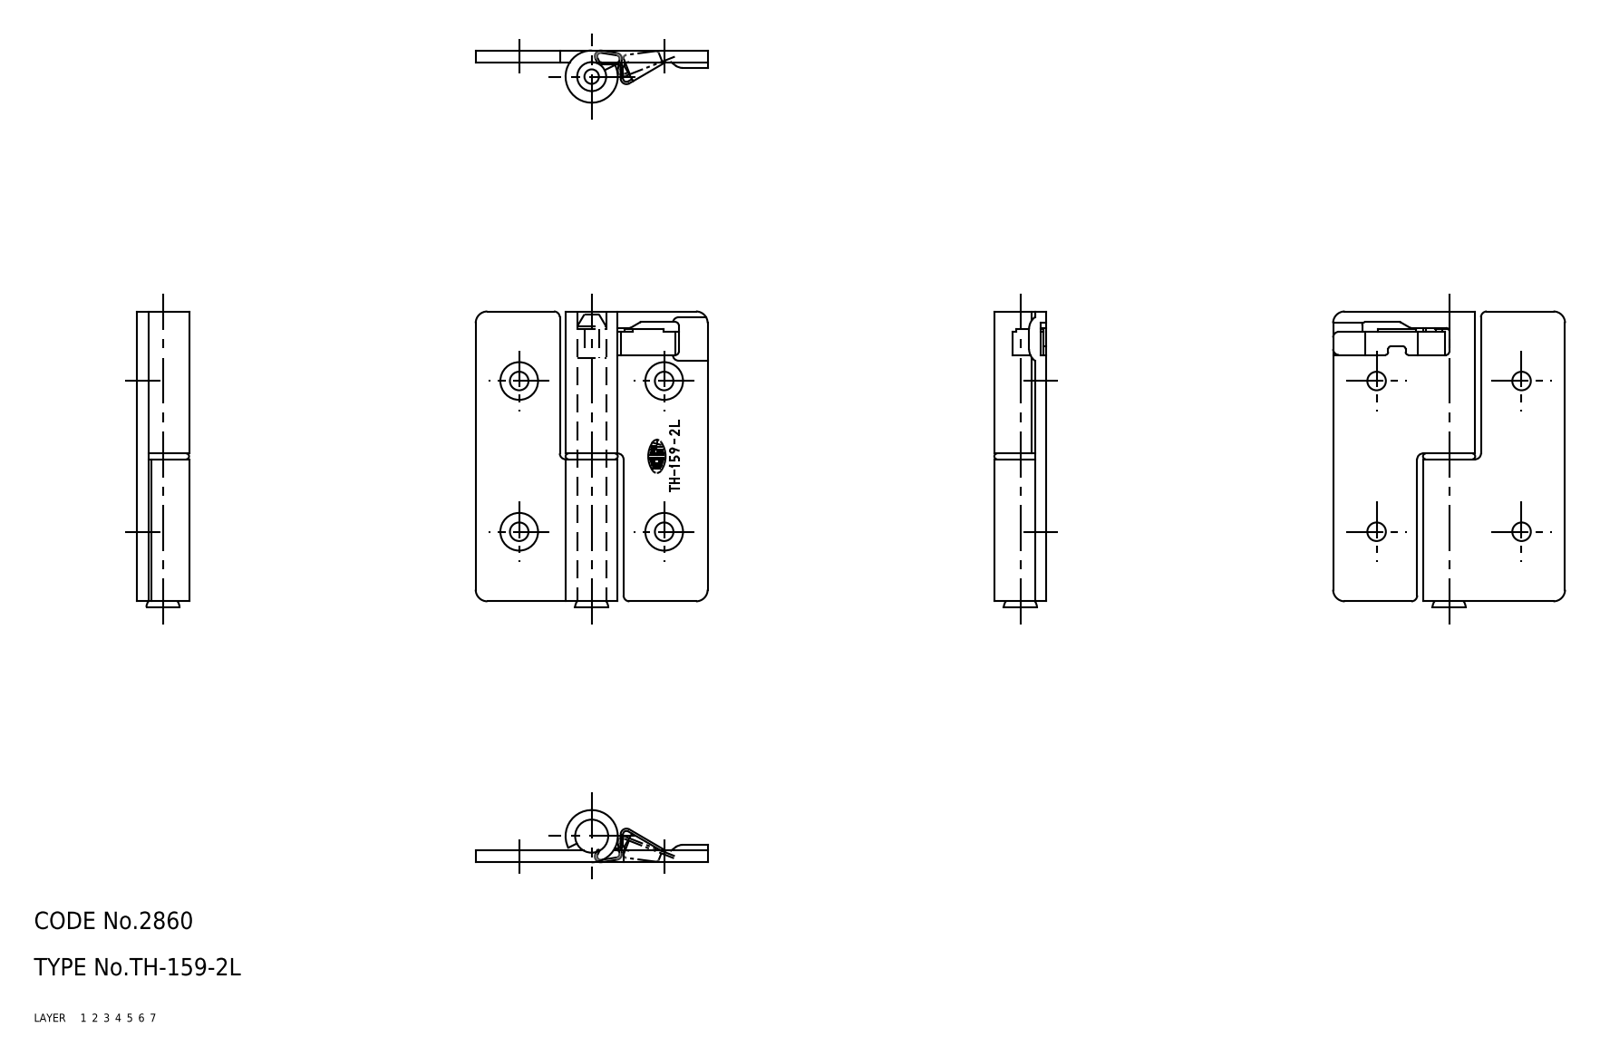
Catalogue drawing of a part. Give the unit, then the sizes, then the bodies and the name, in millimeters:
Units: millimetres
Overall size (bounding box): 51 × 40 × 9
Volume: 5 927 mm³ · Surface area: 7 007 mm²
Bodies: 4 solids, 133 faces (0 planar, 0 cylindrical, 133 other)
Part name (STEP PRODUCT): 67115803; 67115816; 67115829; 67115842
STEP written by: CADfix (AUTOMOTIVE_DESIGN)
